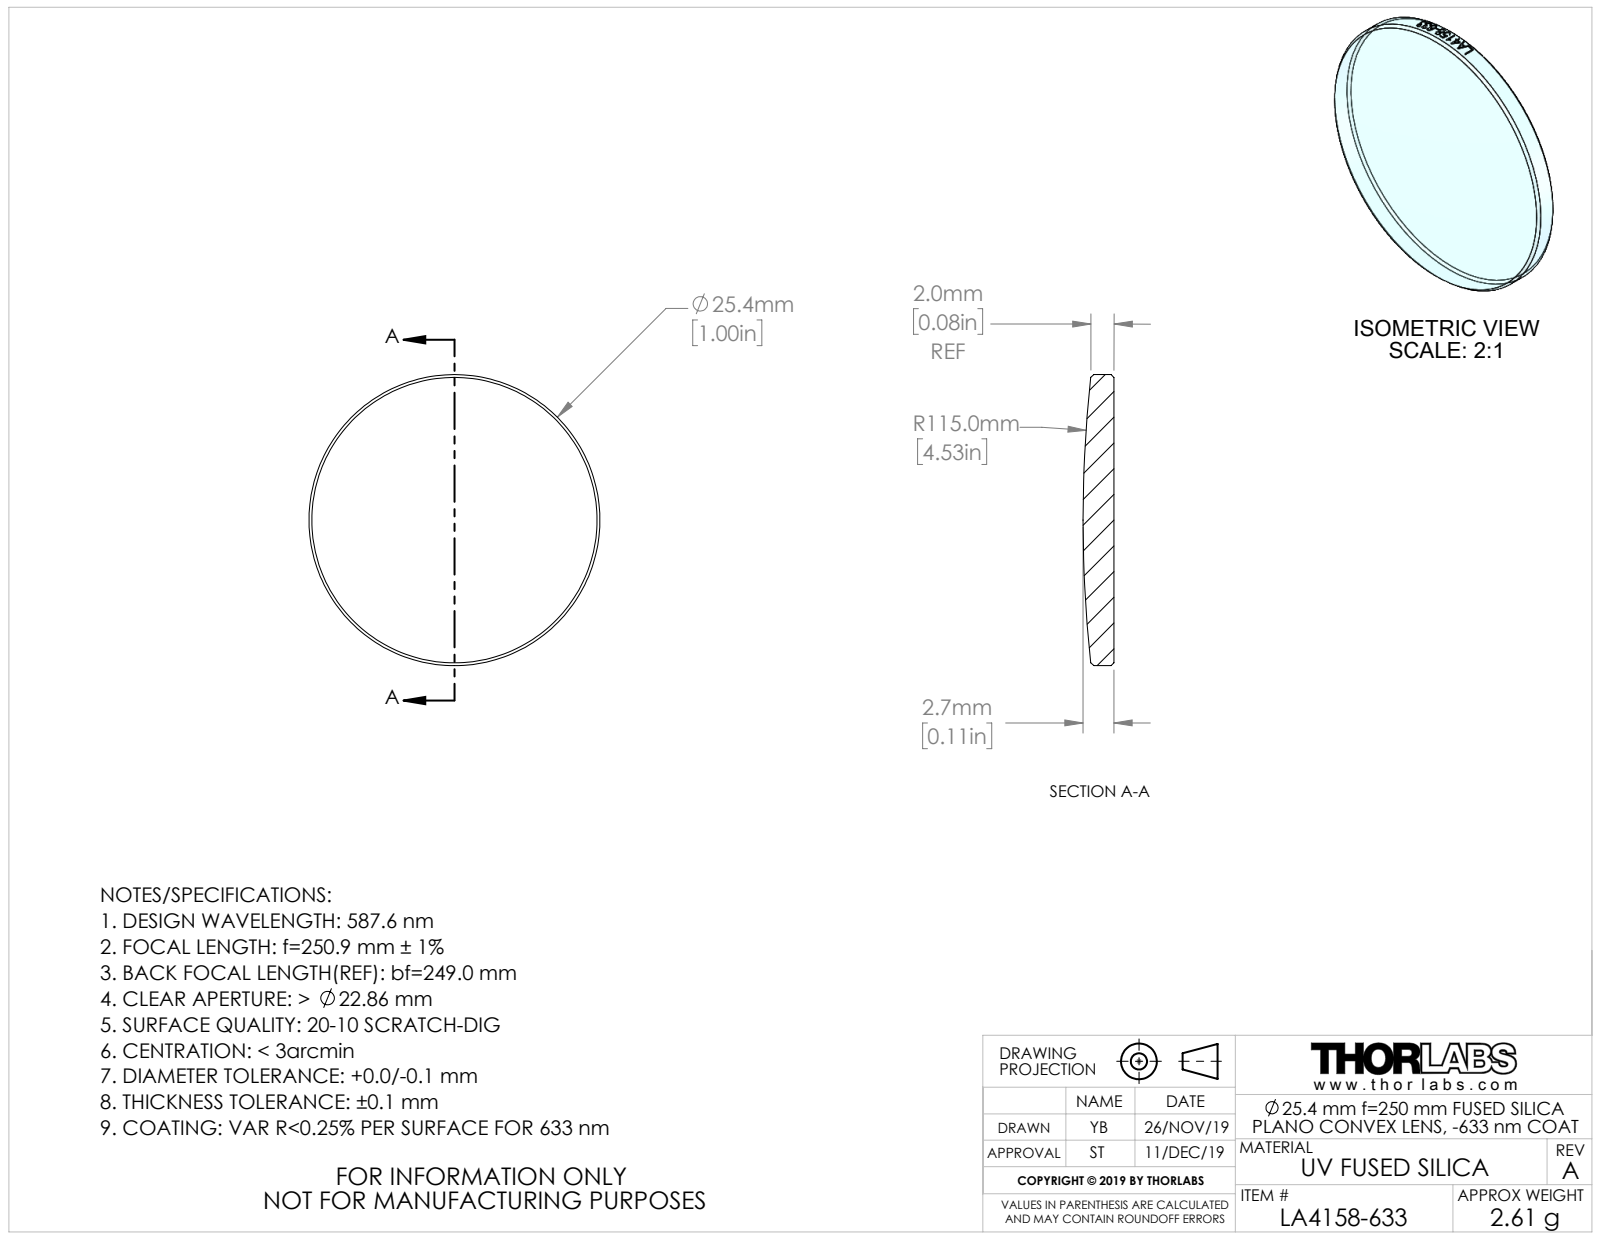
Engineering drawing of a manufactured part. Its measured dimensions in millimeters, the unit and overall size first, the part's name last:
Units: millimetres
Overall size (bounding box): 25.4 × 25.4 × 2.7
Round bosses / shafts (diameter × count): ⌀25.4 ×1
Volume: 1 186 mm³ · Surface area: 1 153 mm²
Bodies: 1 solid, 29 faces (1 planar, 22 cylindrical, 6 other)
Part name (STEP PRODUCT): CTN015016; CTN014997-999
STEP written by: SolidWorks 2018 (AUTOMOTIVE_DESIGN)
